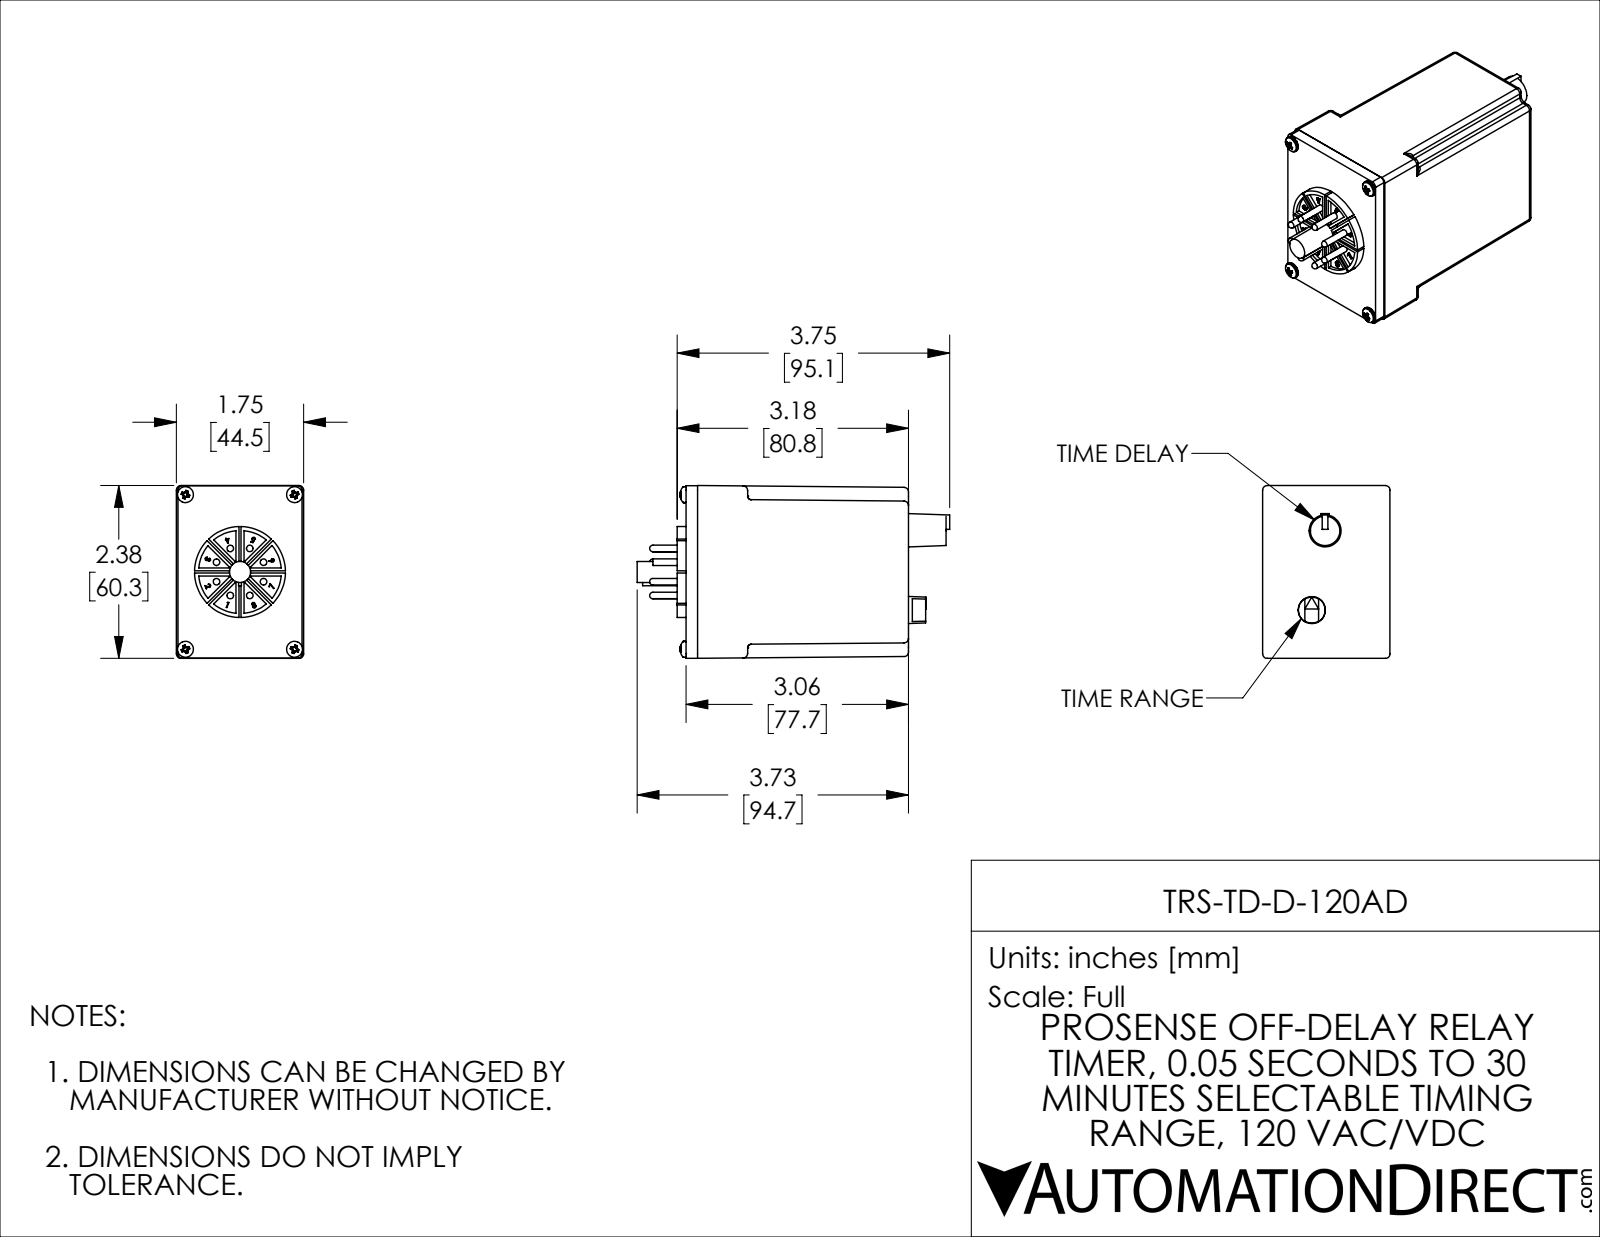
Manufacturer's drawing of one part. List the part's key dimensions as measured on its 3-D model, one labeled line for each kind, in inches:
Part name (STEP PRODUCT): TRS-TD-D-120AD
STEP written by: SolidWorks 2021 (CONFIG_CONTROL_DESIGN)
Units: inches
Bodies: 17 solids, 554 faces (232 planar, 164 cylindrical, 158 other)
Overall size (bounding box): 4.295 × 2.375 × 1.75
Volume: 12.33 in³ · Surface area: 45.99 in²
Round holes (diameter × count): ⌀0.125 ×4
Round bosses / shafts (diameter × count): ⌀0.09 ×8, ⌀0.219 ×4, ⌀1.25 ×1, ⌀0.29 ×1
Partial cylindrical surfaces — rounded edges, fillets, slot ends (radius × count): R0.063 ×32, R0.005 ×8, R0.05 ×4, R0.57 ×1
Main face-to-face distances: 2.9, 0.16, 3.06, 0.07, 0.23, 3.13, 0.188, 0.12, 0.05, 0.28
Hole centre spacings: 1.5, 2.125, 2.601
